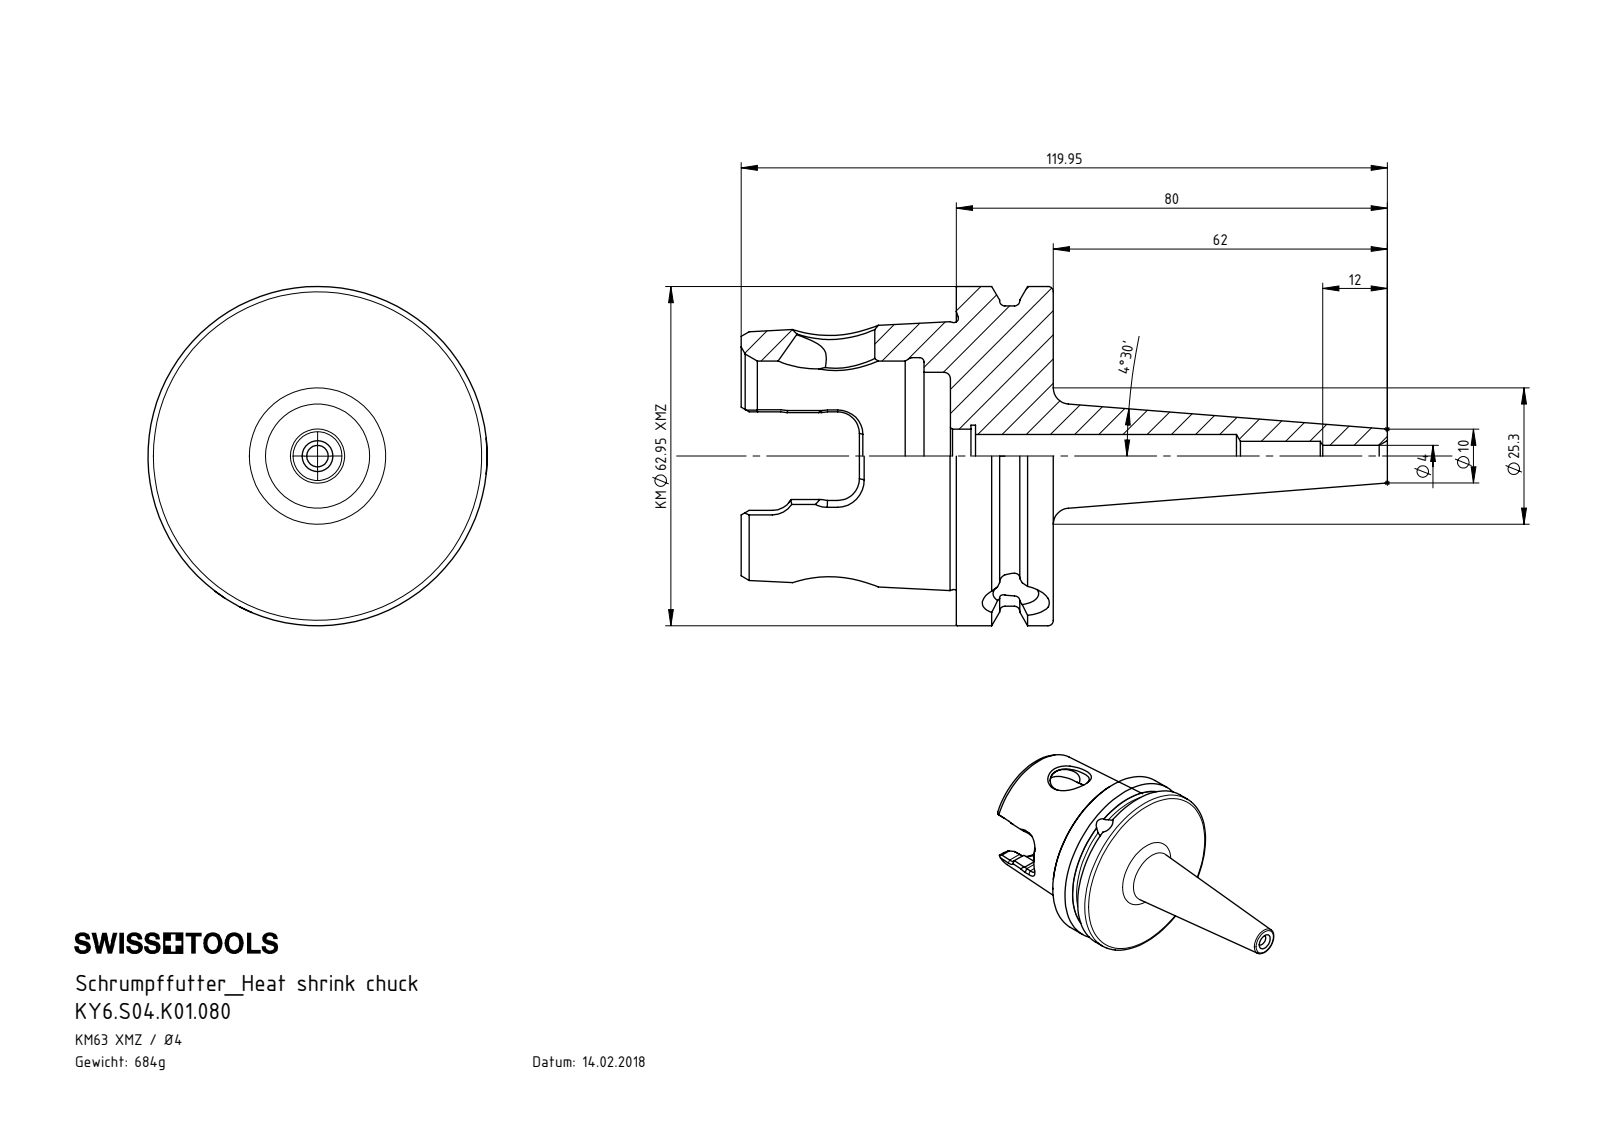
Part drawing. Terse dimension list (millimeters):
name: KY6.S04.K01.080
written by: SolidWorks 2017 (CONFIG_CONTROL_DESIGN)
unit: mm
bodies: 1 solid, 219 faces (45 planar, 51 cylindrical, 123 other)
size: 119.95 × 62.95 × 62.95
volume: 87 163 mm³; area: 24 020 mm²
holes: 2× ⌀7.47, 1× ⌀4, 1× ⌀5.5, 1× ⌀8, 1× ⌀8.48, 1× ⌀10, 1× ⌀11.5, 1× ⌀14.5, 1× ⌀31.1, 1× ⌀35.27, 1× ⌀36.5
bosses: 1× ⌀62.95, 1× ⌀55.7
rounds: 6× R4, 2× R7.04
face distances: 18, 1.1, 19.1, 4.9, 6, 24, 33.95, 38.85, 39.95, 57.95
